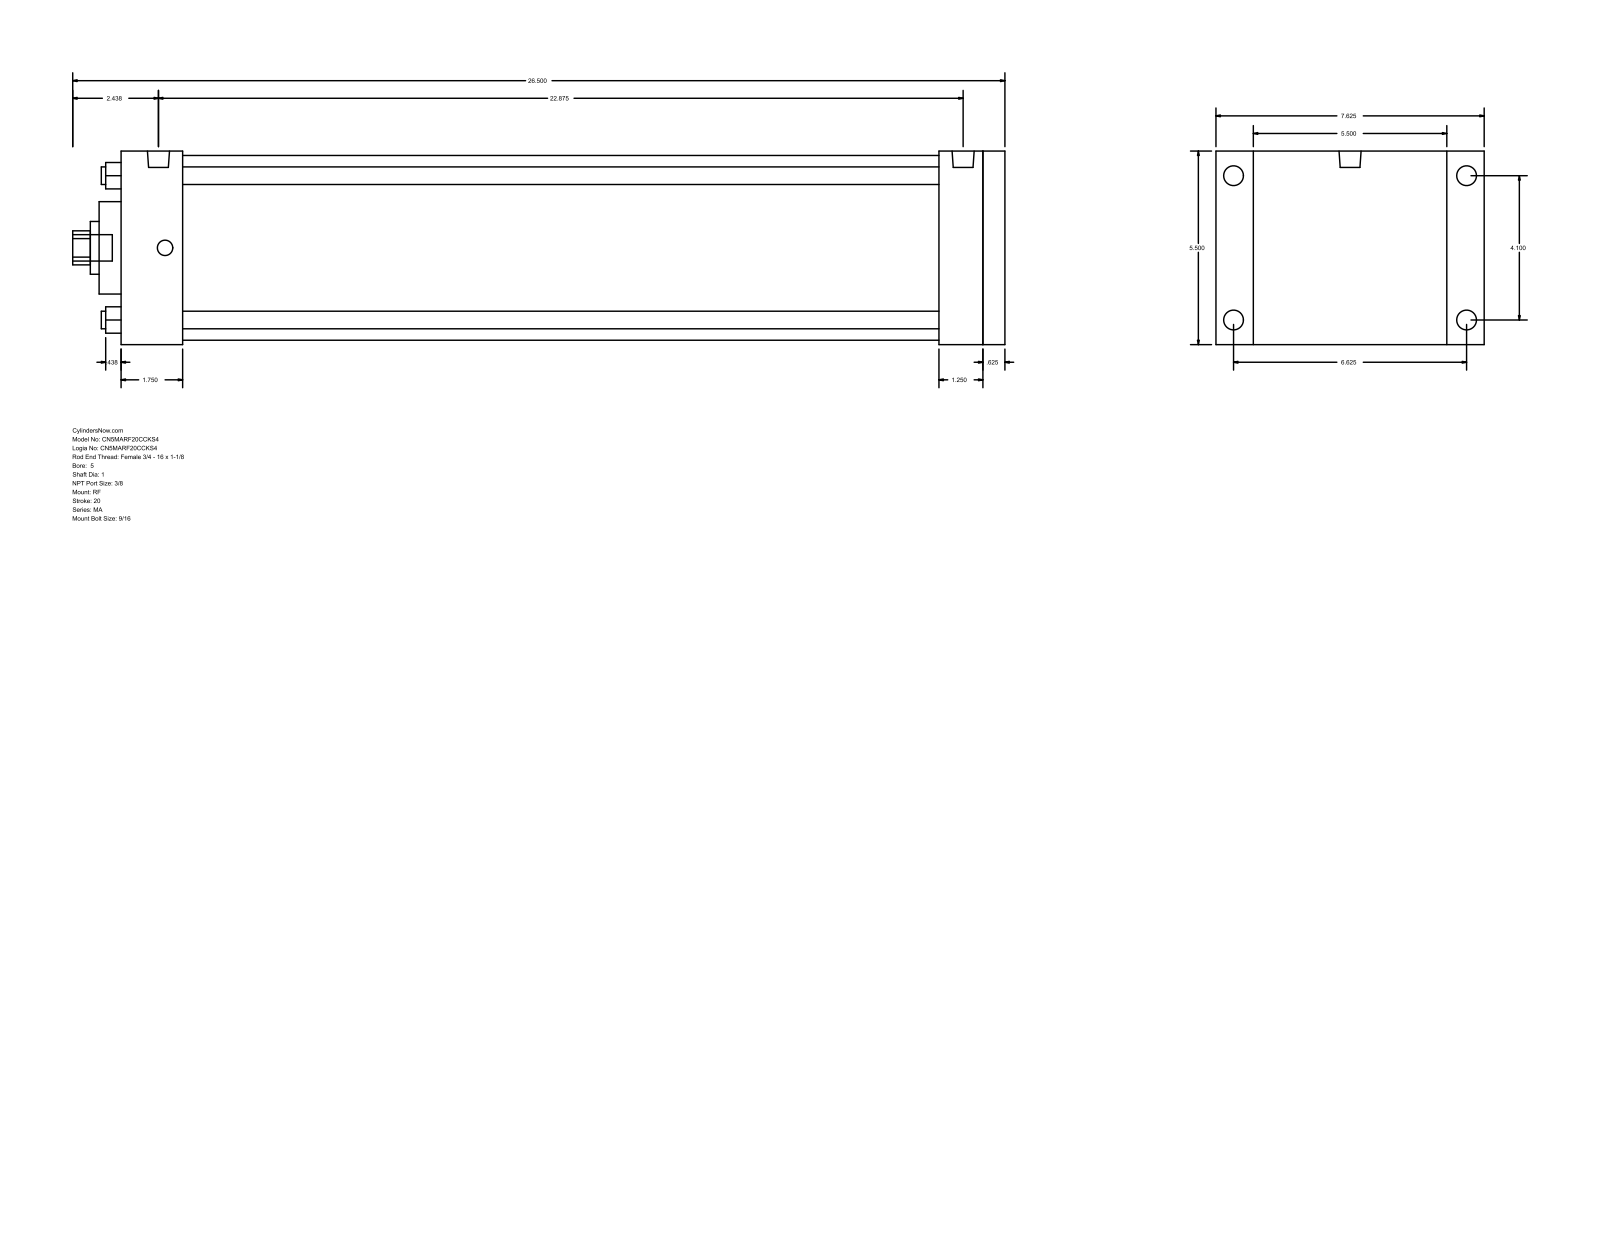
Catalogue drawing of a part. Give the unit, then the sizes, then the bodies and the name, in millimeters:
Units: millimetres
Overall size (bounding box): 673.1 × 193.68 × 139.7
Round holes (diameter × count): ⌀12.7 ×4, ⌀25.4 ×1, ⌀38.1 ×1, ⌀66.67 ×1, ⌀133.35 ×1
Round bosses / shafts (diameter × count): ⌀14.29 ×4, ⌀11.11 ×4, ⌀15.93 ×2, ⌀19.05 ×1
Partial cylindrical surfaces — rounded edges, fillets, slot ends (radius × count): R12.29 ×1
Main face-to-face distances: 139.7, 638.18, 15.87, 622.31, 44.46, 577.85, 593.72, 590.56, 546.1, 31.75
Hole centre spacings: 73.64, 104.14, 147.28
Bodies: 0 solids, 94 faces (65 planar, 29 cylindrical, 0 other)
Part name (STEP PRODUCT): MA_RF__0500_1
STEP written by: GSSL Pune (CONFIG_CONTROL_DESIGN)
